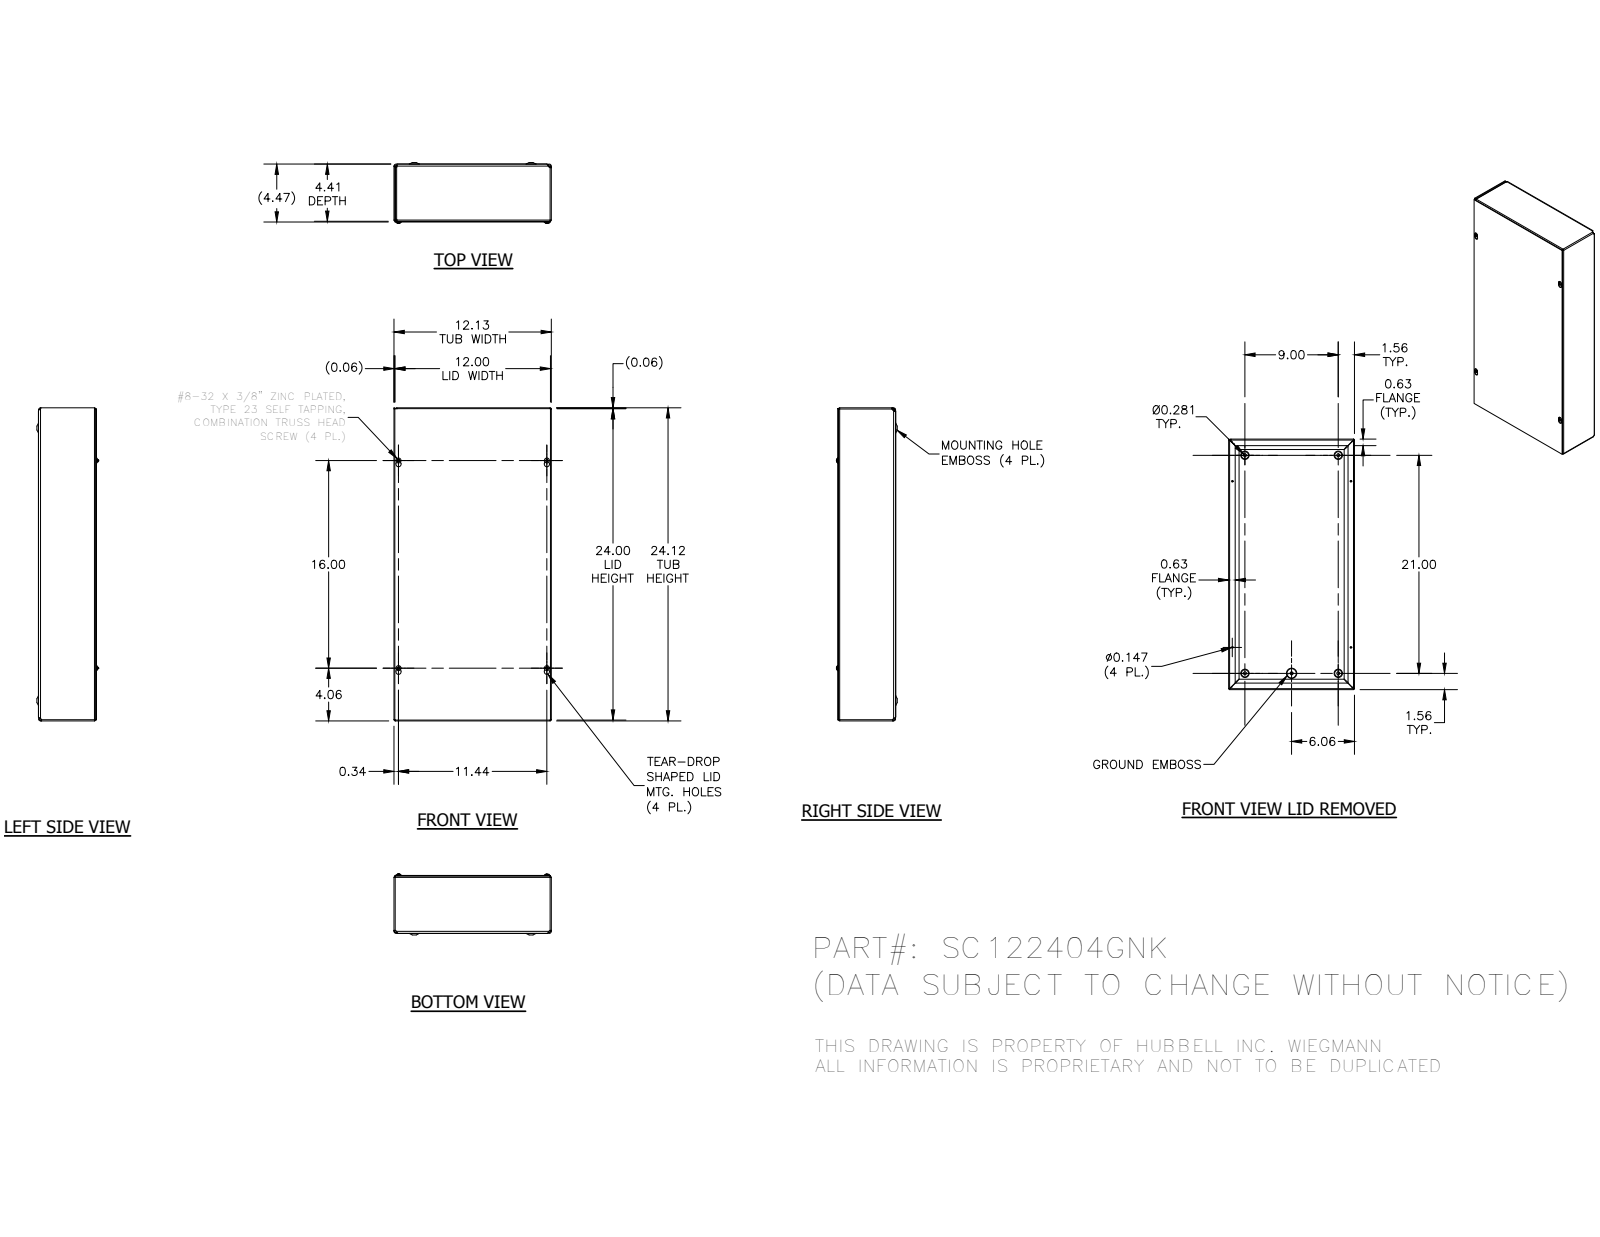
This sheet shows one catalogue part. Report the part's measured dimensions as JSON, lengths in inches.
{"part_name": "SC1224GNKBKP; SC122404GNKWRA; SC1224GNKLID; 34056 (+1 more)", "step_written_by": "Autodesk Inventor 2014 (AUTOMOTIVE_DESIGN)", "units": "inches", "bodies": {"solids": 7, "faces": 358, "planar": 133, "cylindrical": 73, "other": 152}, "overall_size": [24.125, 12.125, 4.693], "volume_in3": 61, "surface_area_in2": 1984, "round_holes": [[0.147, 4], [0.3, 4], [0.165, 1]], "round_bosses_or_shafts": [[0.384, 4], [0.164, 4], [0.228, 1]], "partial_cylinders_radius": [[0.031, 8], [0.093, 8], [0.055, 4], [0.062, 4], [0.094, 4], [0.117, 4], [0.124, 4], [0.125, 4]], "face_to_face_distances": [0.062, 4.343, 4.405, 0.063, 4.406, 4.468, 0.062, 12.125, 12.063, 12.063], "hole_center_spacings": [2.782, 4.5, 9, 10.52, 11.437, 16, 18.539, 18.541]}
